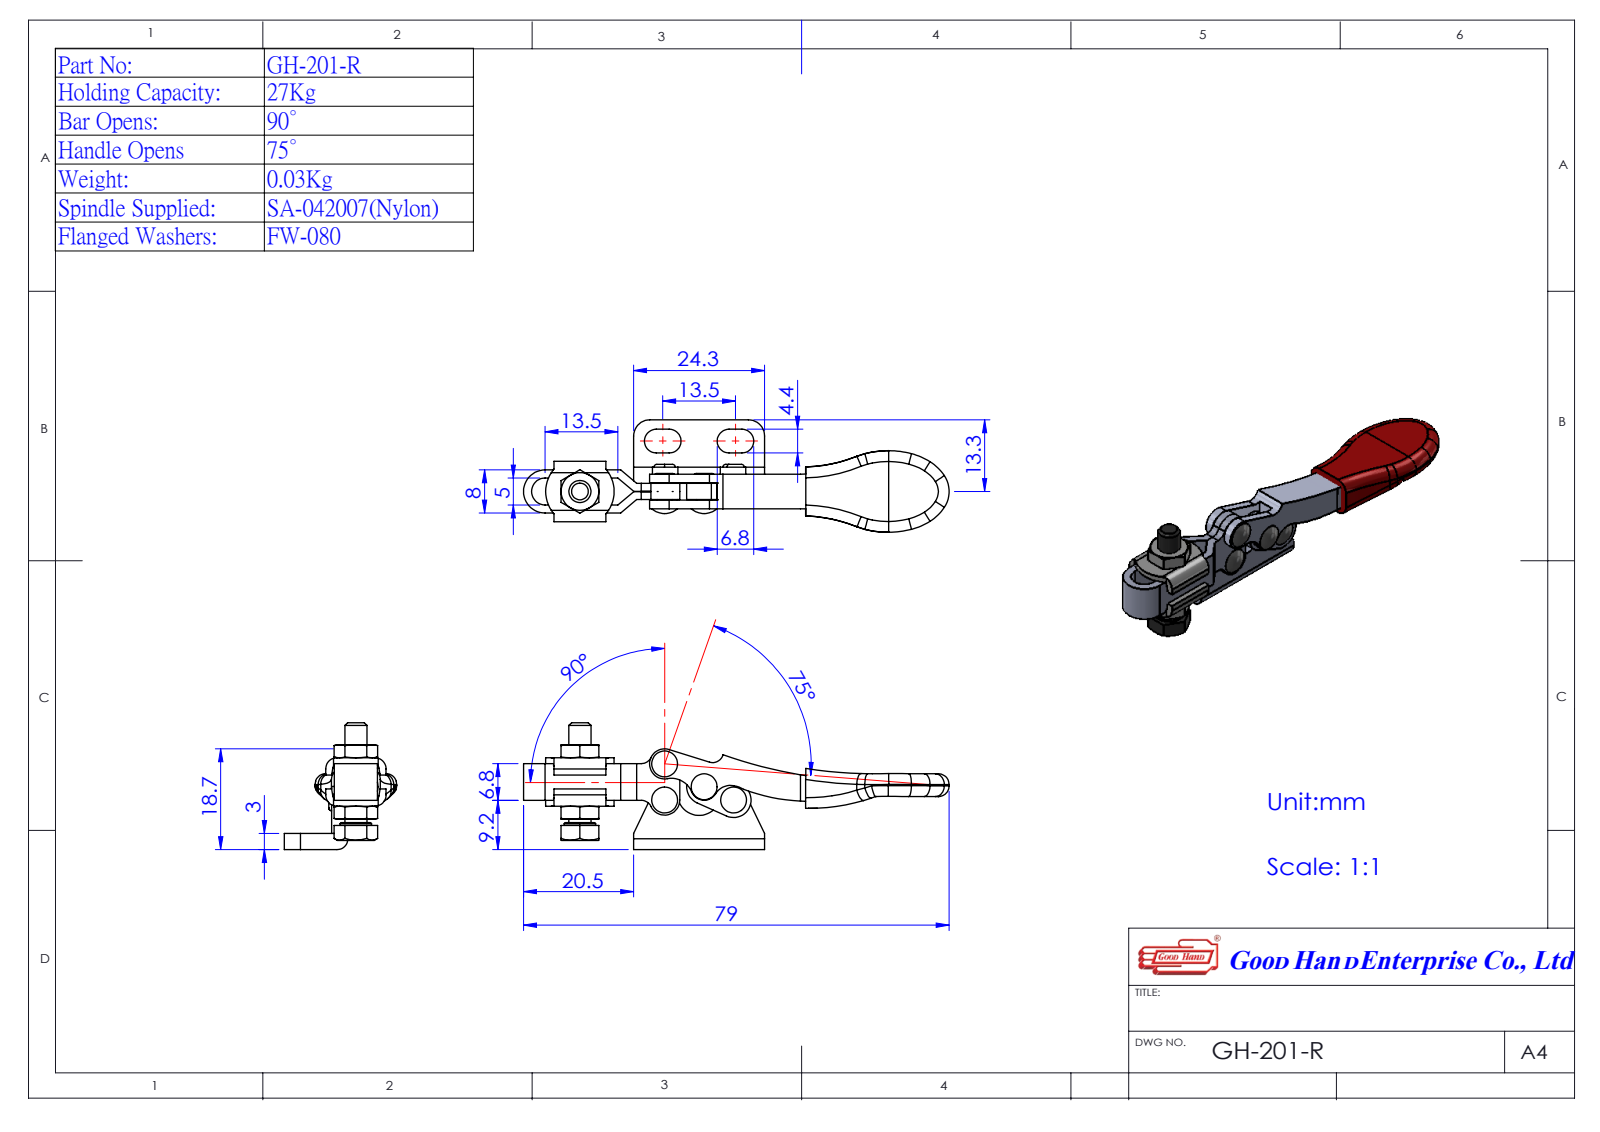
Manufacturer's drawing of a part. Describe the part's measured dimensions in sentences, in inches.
The part is named "Group1^GH-201-R(簡化); 1201AL13-1^GH-201-R(簡化); GH-201-R(簡化); Group2^GH-201-R(簡化) (+2 more)". Its 3-D file was written by "SolidWorks 2016 (AUTOMOTIVE_DESIGN)". It is 6 solids with 318 faces: 118 planar, 141 cylindrical and 59 other. Overall it measures 3.111 by 0.927 by 0.822 inches. Its volume is 0.173 cubic inches and its surface area 10.18 square inches. Round holes: 4 of diameter 0.091. Round bosses or shafts: 2 of diameter 0.085, 1 of diameter 0.228, 1 of diameter 0.161, 1 of diameter 0.11. Partial cylindrical surfaces (rounded edges, fillets, slot ends): 4 of radius 0.039, 4 of radius 0.083, 4 of radius 0.087, 4 of radius 0.433, 4 of radius 0.485, 3 of radius 0.079, 3 of radius 0.157, 2 of radius 0.098. The main face-to-face distances are 0.059, 0.118, 0.157, 0.063, 0.098, 0.126, 0.067, 0.185, 0.283, 0.094. The hole center spacings are 0.236, 0.264, 0.304, 0.333, 0.504, 0.569.
